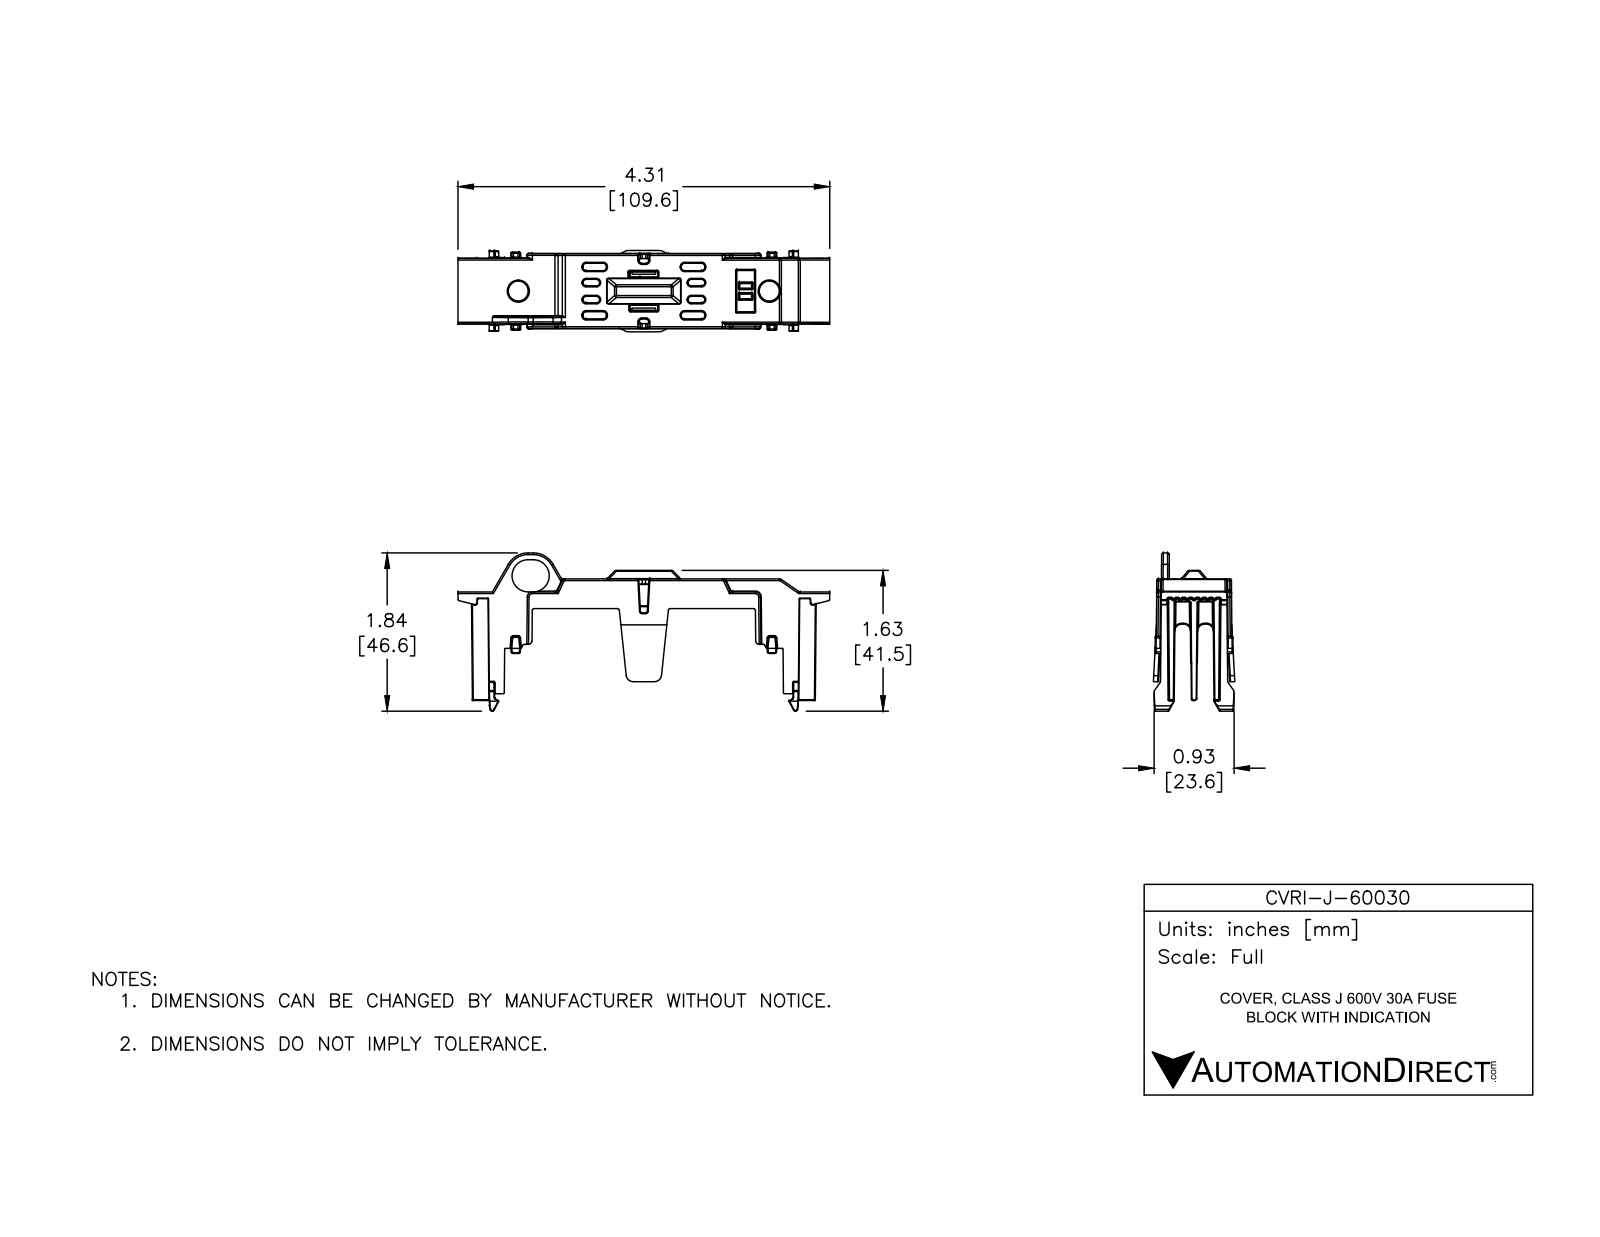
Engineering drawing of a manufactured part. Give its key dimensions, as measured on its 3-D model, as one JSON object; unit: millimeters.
{"part_name": "CVRI-J-60030", "step_written_by": "SolidWorks 2016 (AUTOMOTIVE_DESIGN)", "units": "millimeters", "bodies": {"solids": 1, "faces": 2037, "planar": 407, "cylindrical": 912, "other": 718}, "overall_size": [109.6, 46.6, 24], "volume_mm3": 11300, "surface_area_mm2": 15230, "partial_cylinders_radius": [[0.3, 299], [0.2, 239], [0.5, 58], [1, 50], [0.8, 8], [2, 6], [0.1, 4], [0.7, 2]], "face_to_face_distances": [1.5, 1.4, 2.9, 3.9, 1.5, 5.5, 2.6, 3.9, 4.1, 2.4]}
